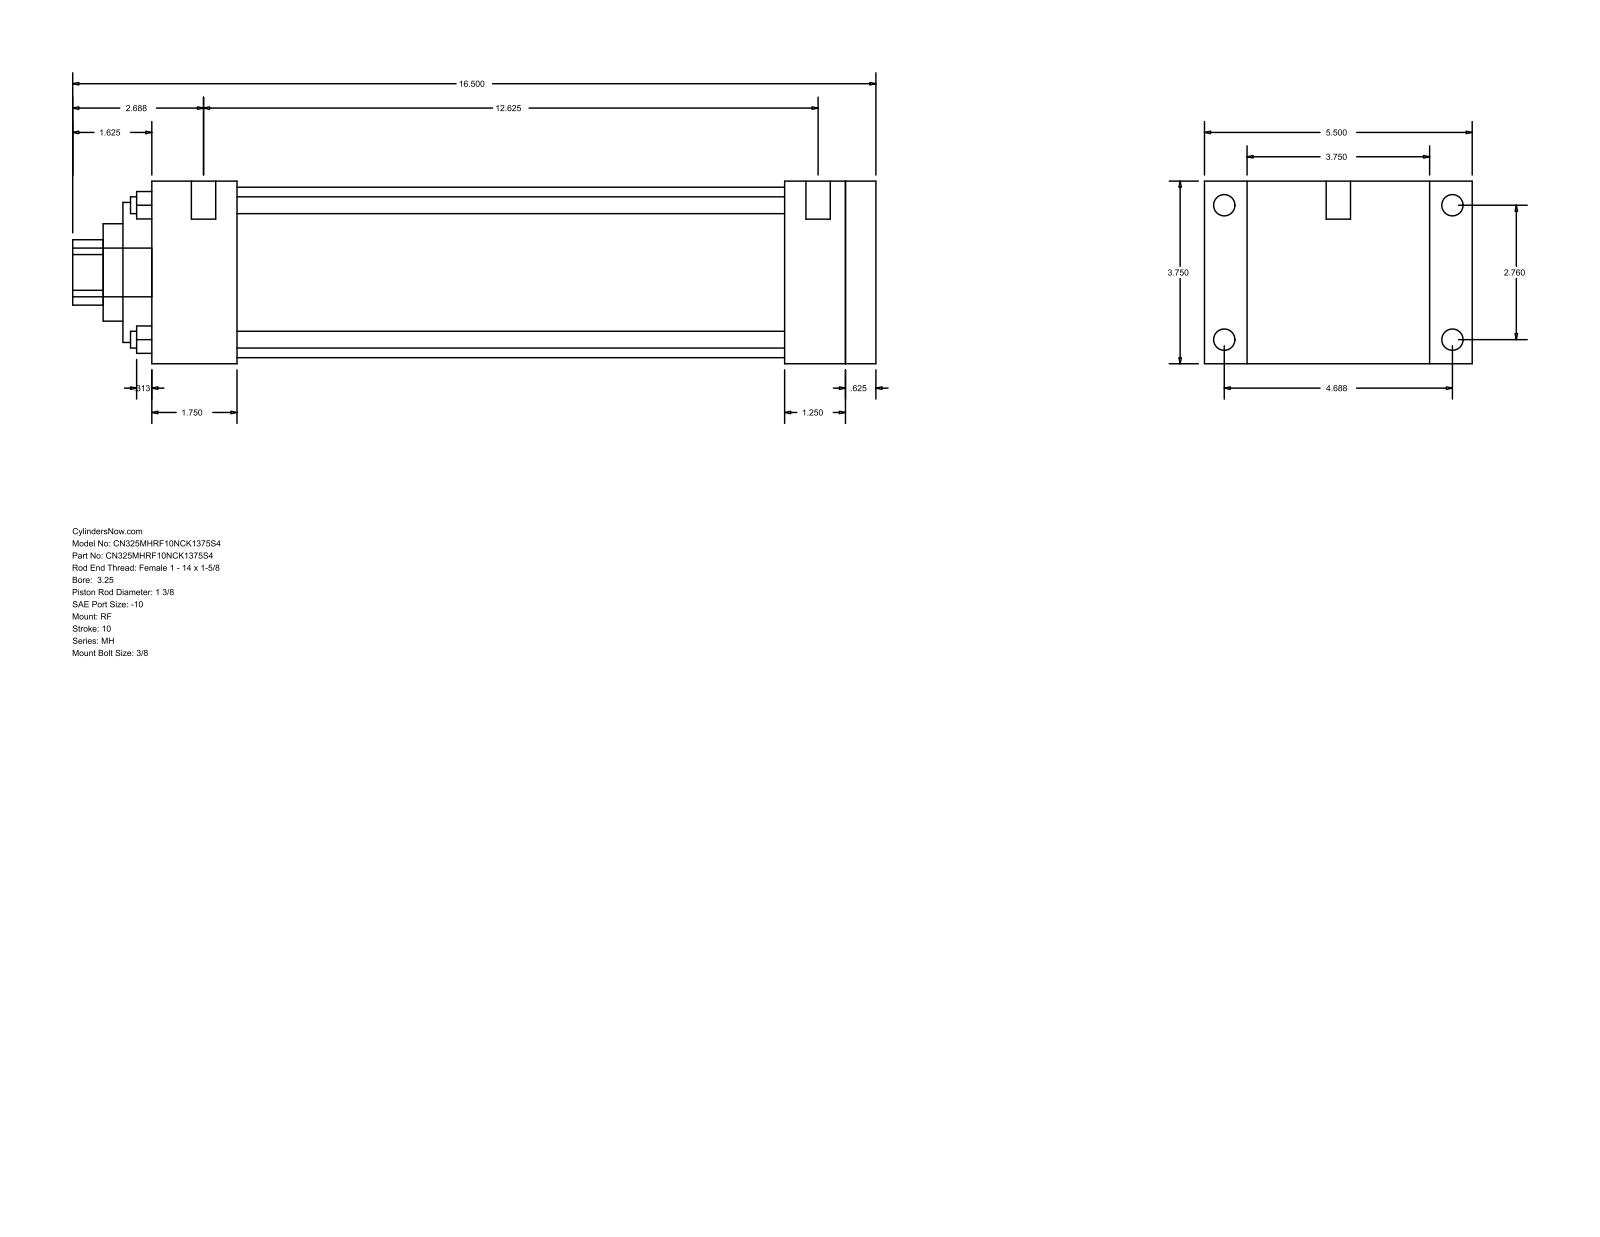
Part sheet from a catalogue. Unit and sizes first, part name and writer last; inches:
Units: inches
Overall size (bounding box): 16.5 × 5.5 × 3.75
Round holes (diameter × count): ⌀0.345 ×4, ⌀1.375 ×1, ⌀2 ×1, ⌀2.875 ×1, ⌀3.5 ×1
Round bosses / shafts (diameter × count): ⌀0.438 ×4, ⌀0.219 ×4, ⌀0.5 ×2, ⌀1 ×1
Partial cylindrical surfaces — rounded edges, fillets, slot ends (radius × count): R0.672 ×1
Main face-to-face distances: 3.75, 14.875, 14.25, 0.625, 0.875, 4.625, 1.75, 12.5, 13.125, 13
Hole centre spacings: 1.952, 2.76, 3.903
Bodies: 0 solids, 94 faces (65 planar, 29 cylindrical, 0 other)
Part name (STEP PRODUCT): MH_RF__0325_1.375
STEP written by: GSSL Pune (CONFIG_CONTROL_DESIGN)
